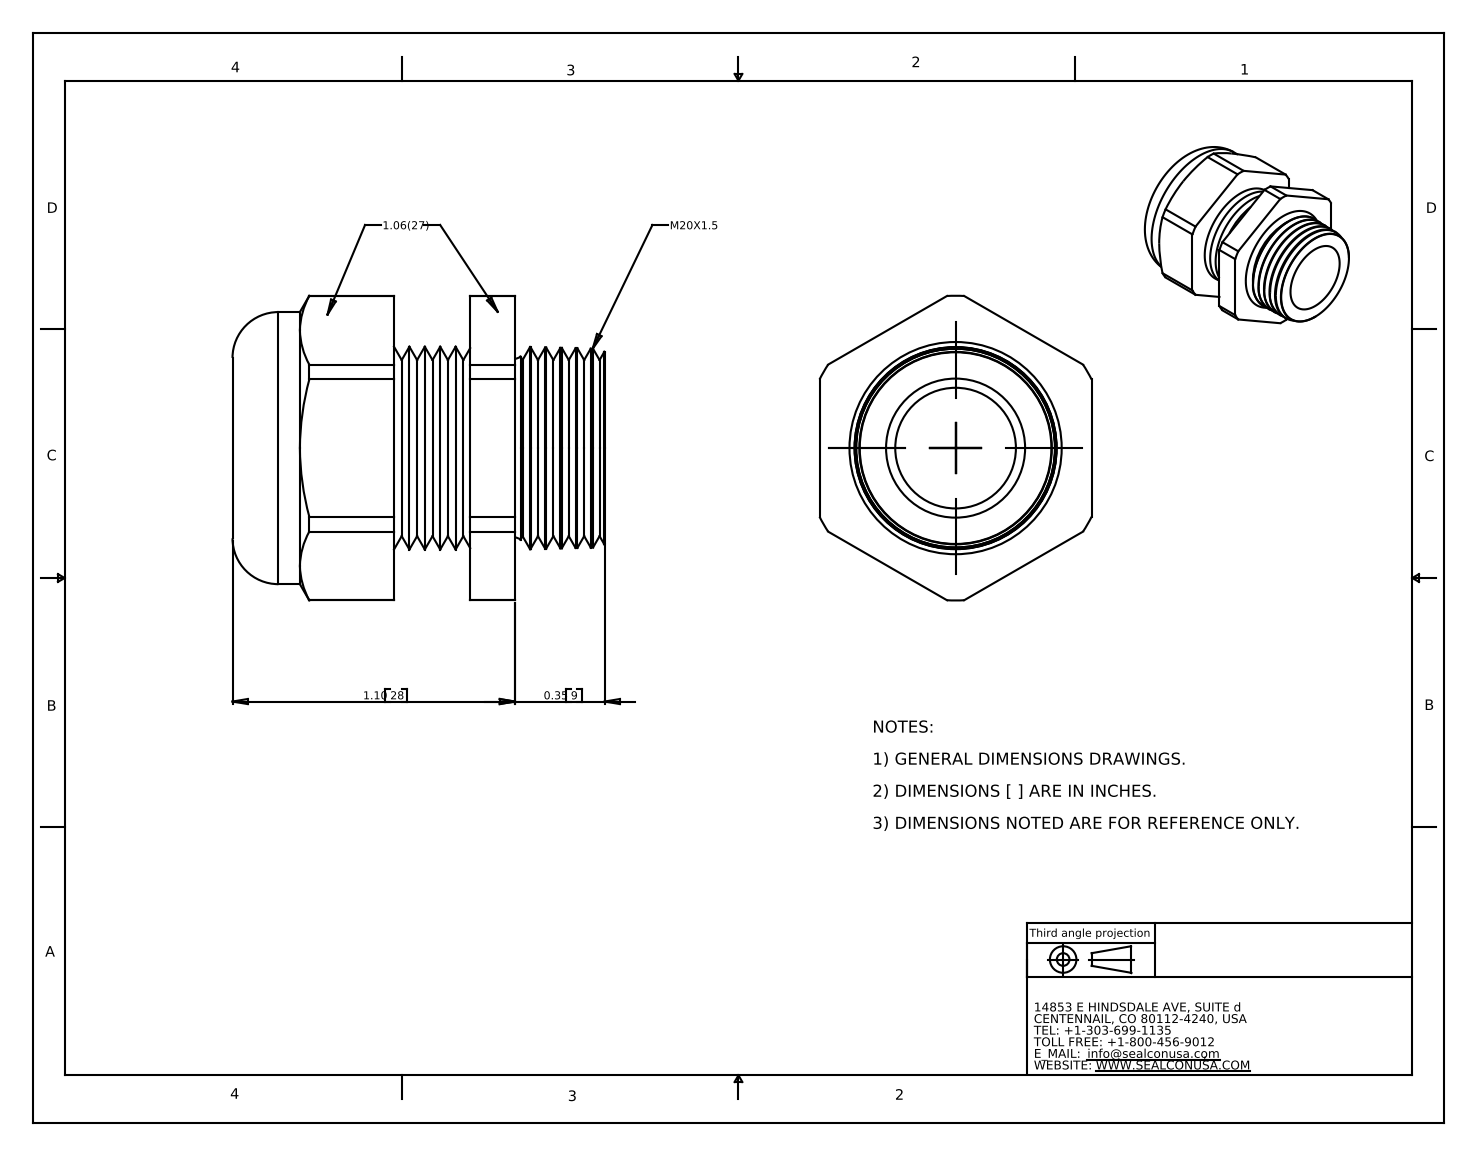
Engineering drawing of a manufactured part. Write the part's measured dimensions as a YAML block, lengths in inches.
part_name: "CD22MR-GY"
step_written_by: "SolidWorks 2007 (CONFIG_CONTROL_DESIGN)"
units: inches
bodies: {solids: 2, faces: 116, planar: 20, cylindrical: 24, other: 72}
overall_size: [1.45, 1.187, 1.06]
volume: 0.725
surface_area: 11.64
round_holes:
  - {diameter: 0.47, count: 1}
  - {diameter: 0.671, count: 1}
  - {diameter: 0.79, count: 1}
round_bosses_or_shafts:
  - {diameter: 1.06, count: 1}
partial_cylinders:
  - {radius: 0.594, count: 1}
face_to_face_distances: [1.06, 0.297, 0.471, 0.174, 0.367, 0.663, 0.837, 1.187, 0.821, 0.524]
